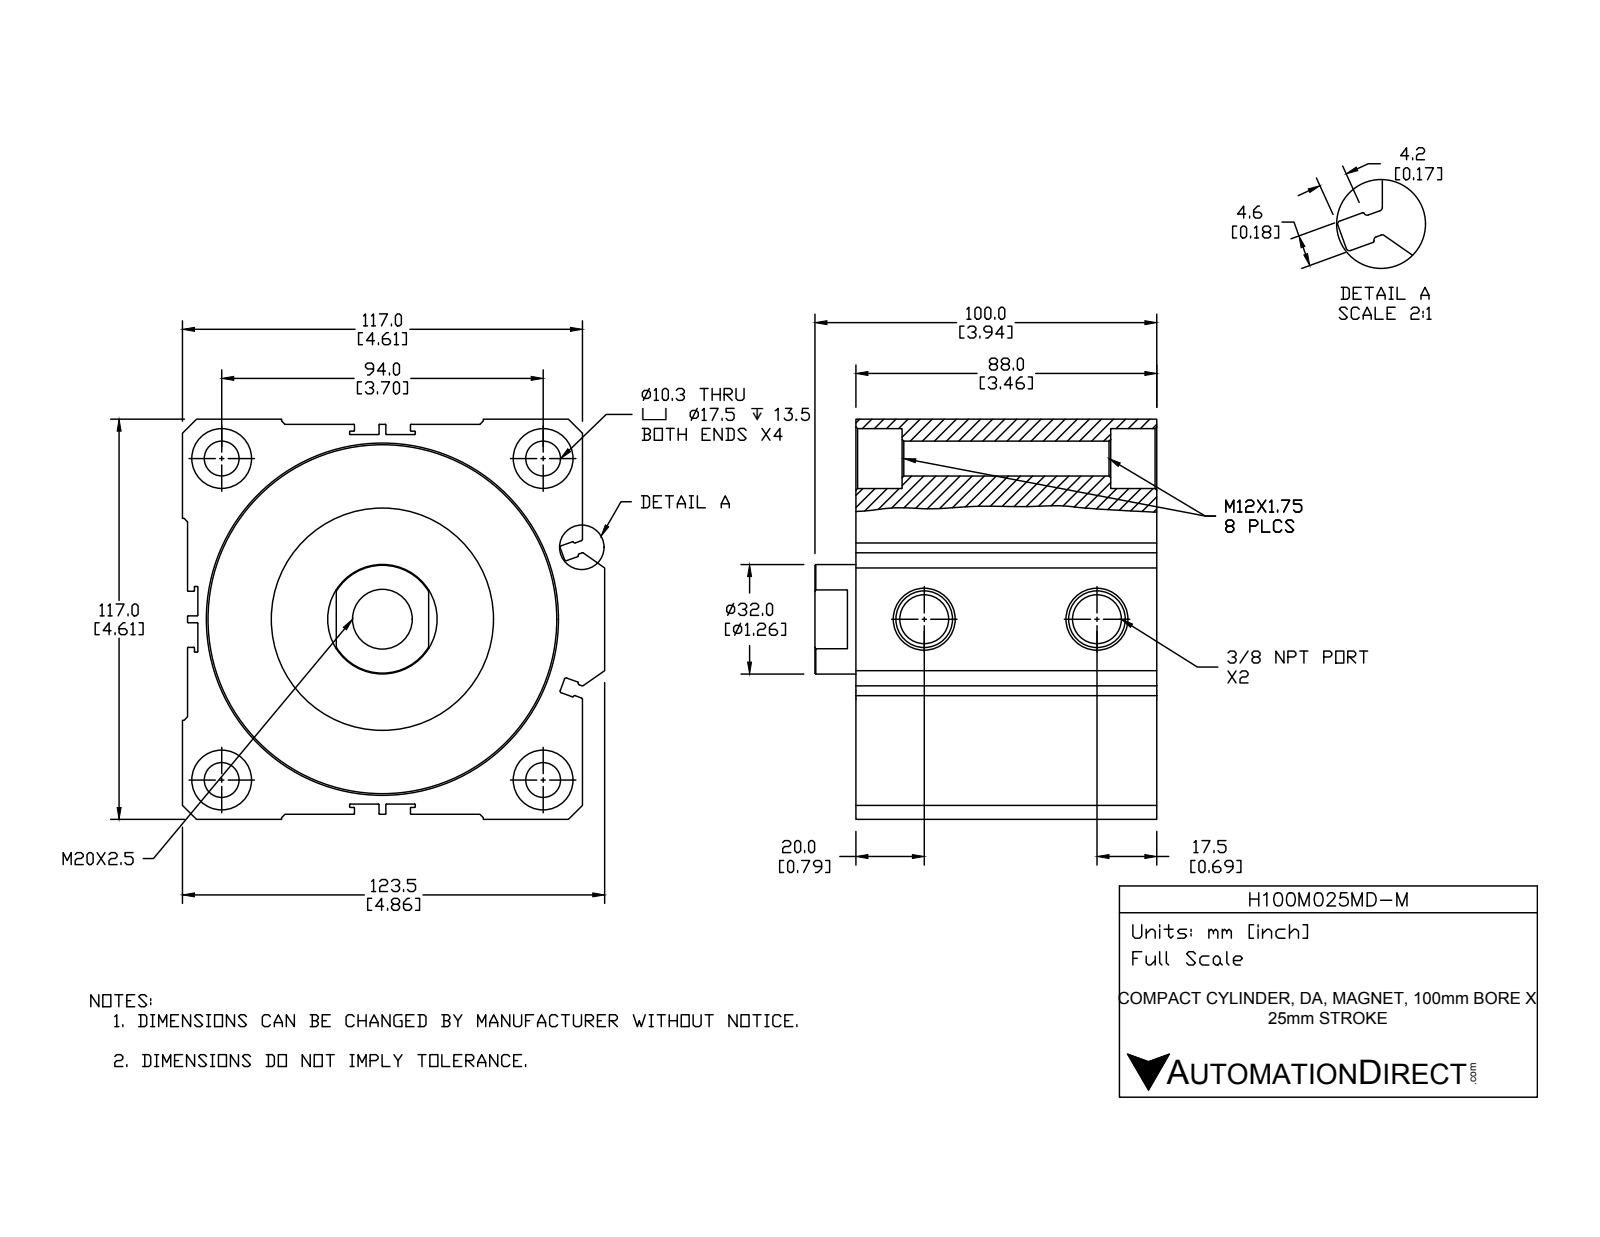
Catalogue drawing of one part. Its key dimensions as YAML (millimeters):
part_name: "H100M025MD-M; H100M025MD-M-BODY; H100M025MD-M-PISTON"
step_written_by: "SolidWorks 2015 (CONFIG_CONTROL_DESIGN)"
units: millimeters
bodies: {solids: 2, faces: 261, planar: 105, cylindrical: 103, other: 53}
overall_size: [123.5, 117, 100]
volume: 887499
surface_area: 159591
round_holes:
  - {diameter: 17.5, count: 5}
  - {diameter: 10.2, count: 4}
  - {diameter: 14.27, count: 2}
  - {diameter: 32, count: 1}
  - {diameter: 65, count: 1}
  - {diameter: 100, count: 1}
  - {diameter: 102, count: 1}
round_bosses_or_shafts:
  - {diameter: 39, count: 1}
partial_cylinders:
  - {radius: 0.2, count: 40}
  - {radius: 0.5, count: 12}
face_to_face_distances: [1.5, 115.5, 117, 27.8, 53.5, 25.7, 66, 12.5, 40.3, 12]
hole_center_spacings: [66.47, 94, 132.94, 50.5]
